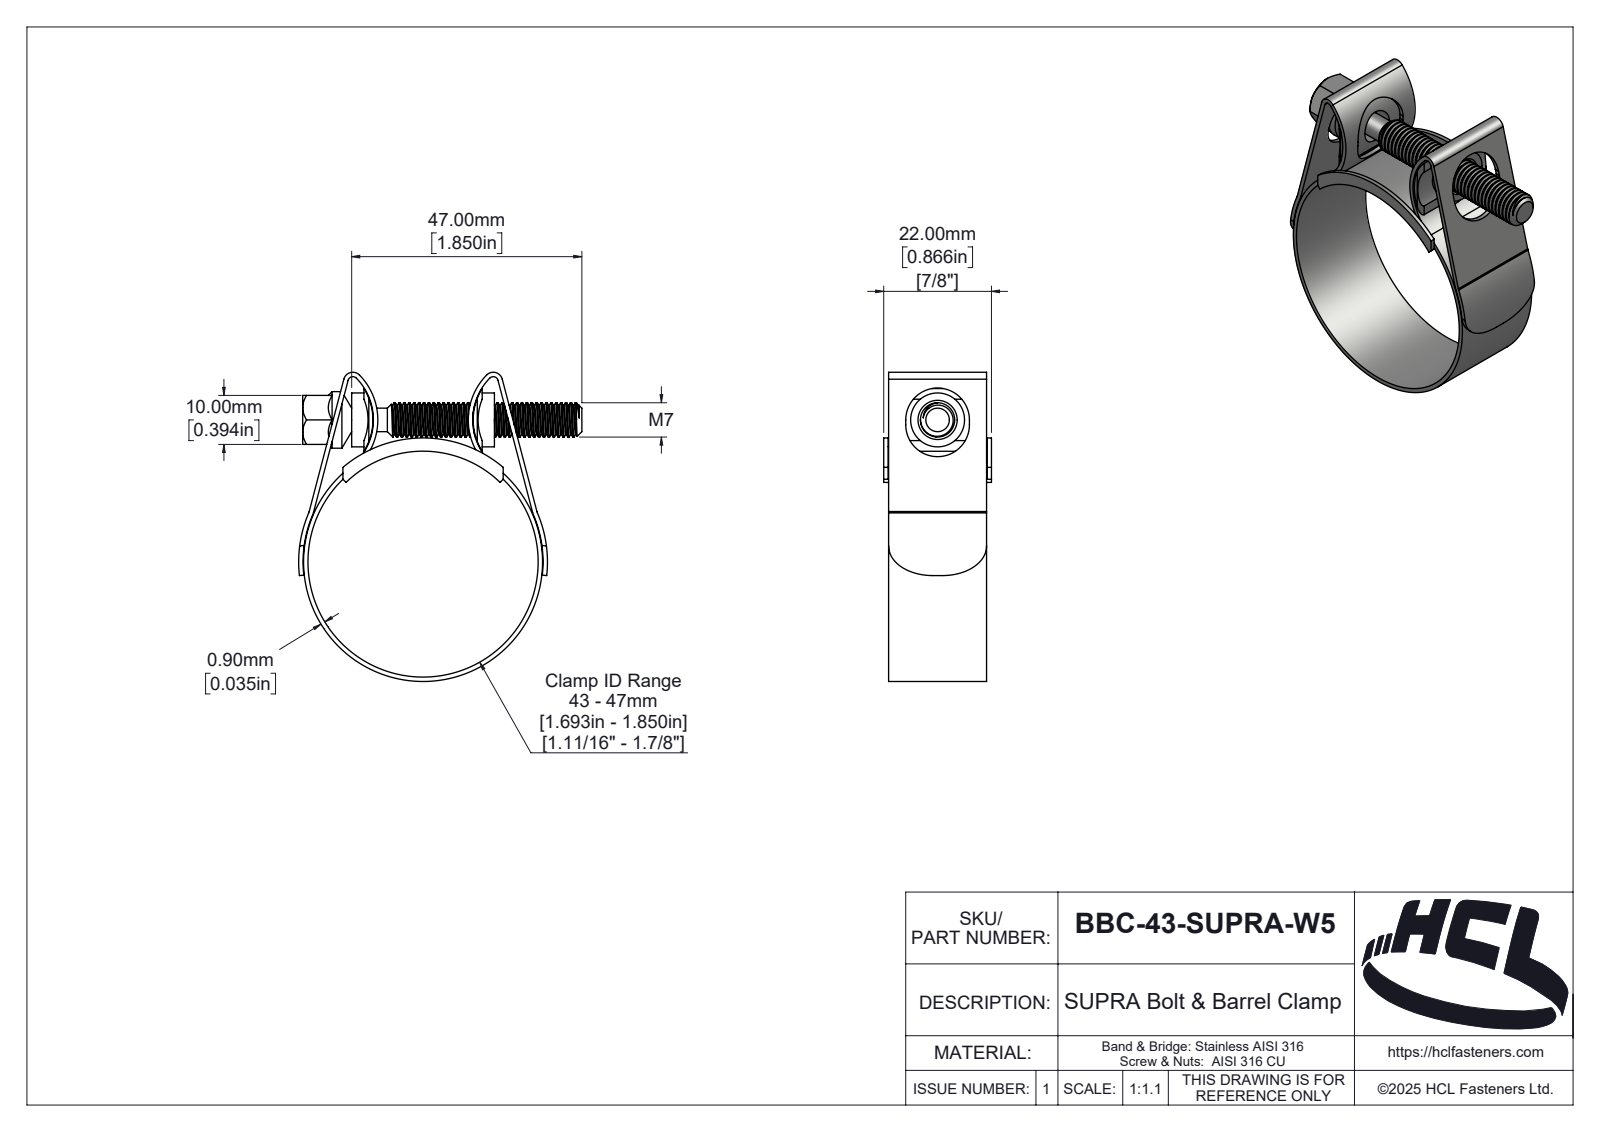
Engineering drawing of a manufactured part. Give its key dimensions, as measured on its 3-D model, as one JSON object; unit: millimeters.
{"part_name": "BBC-43-SUPRA-W5", "step_written_by": "SolidWorks 2025 (AUTOMOTIVE_DESIGN)", "units": "millimeters", "bodies": {"solids": 5, "faces": 314, "planar": 46, "cylindrical": 189, "other": 79}, "overall_size": [63.11, 57.83, 22], "volume_mm3": 7697, "surface_area_mm2": 14445, "round_holes": [[47, 1]], "round_bosses_or_shafts": [[11.55, 1], [11, 1], [7, 1], [4.8, 1]], "partial_cylinders_radius": [[1, 6], [1.9, 2], [2, 2], [2.9, 2], [6.5, 2], [11.07, 2], [12.07, 2], [12.17, 2]], "face_to_face_distances": [0.9, 20, 1, 21, 10, 21.1, 20.1, 22, 2.5, 26.64]}
